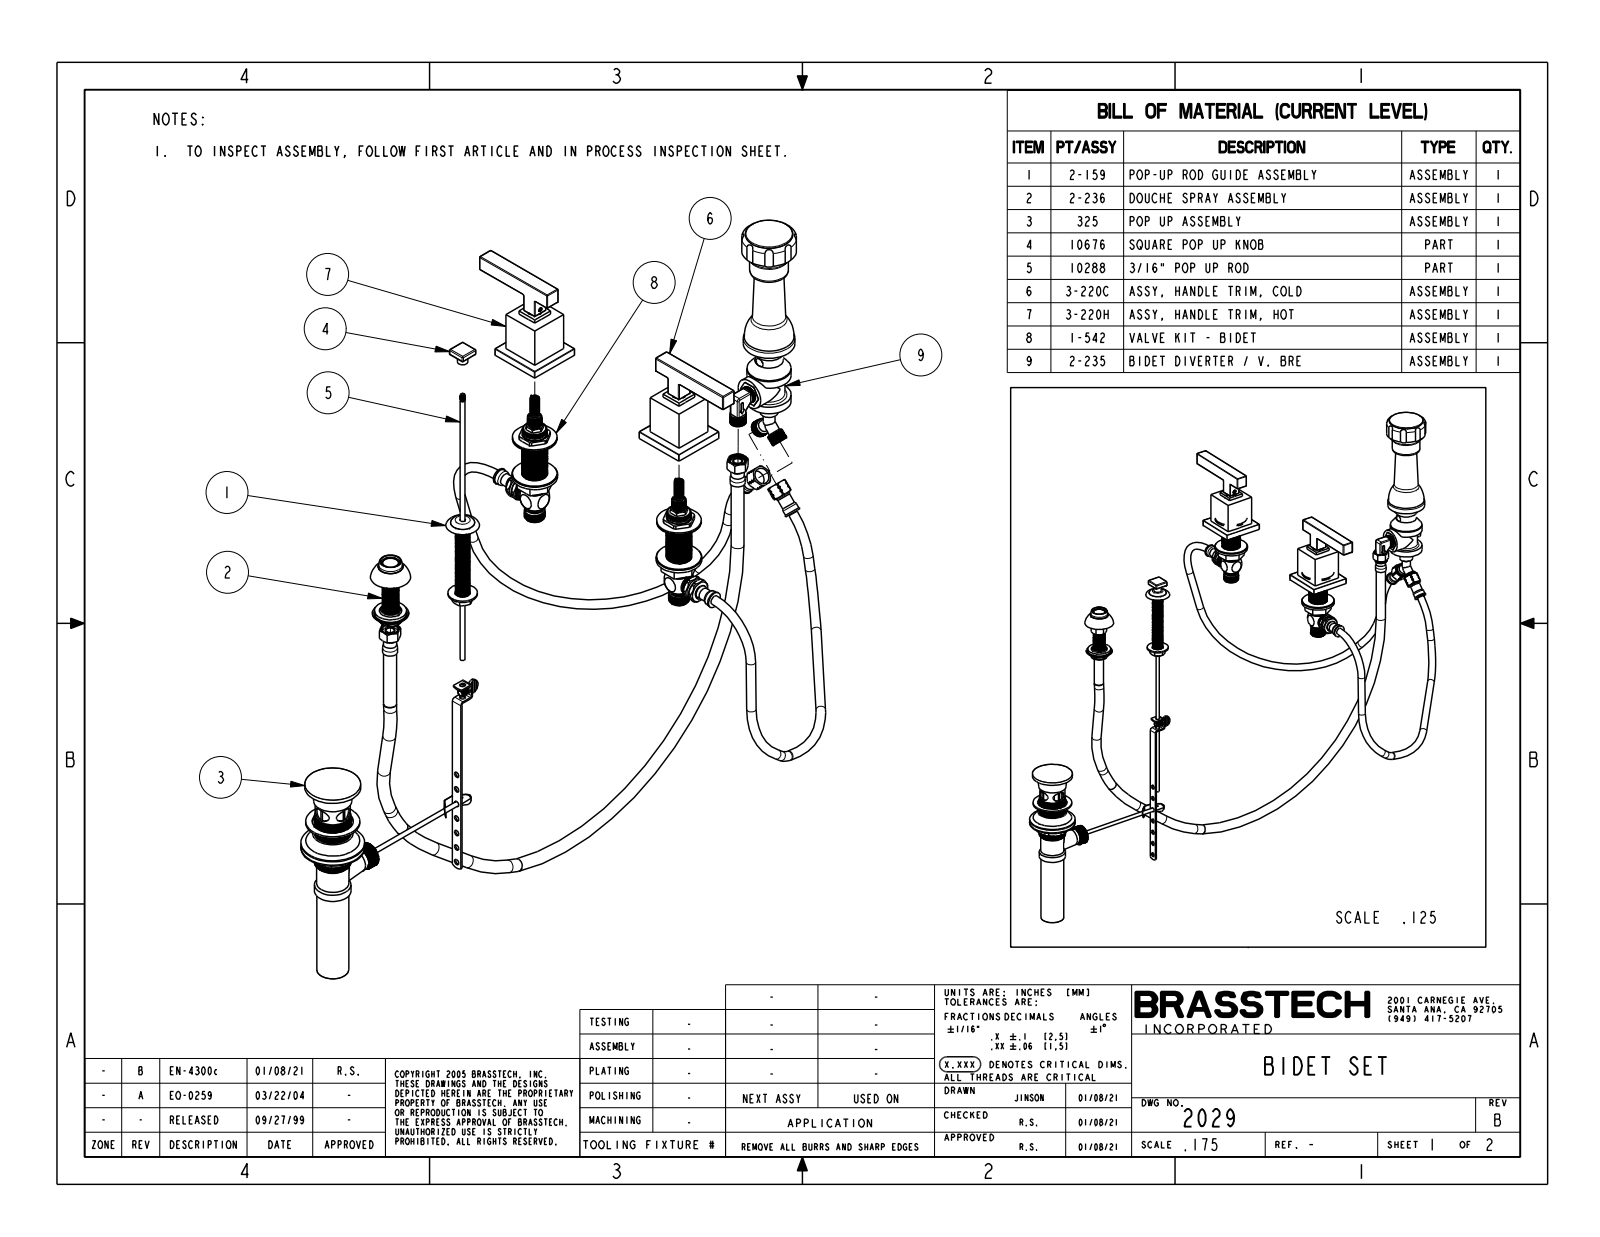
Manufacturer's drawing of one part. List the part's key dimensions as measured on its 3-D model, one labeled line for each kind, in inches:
Part name (STEP PRODUCT): 2029
STEP written by: CREO PARAMETRIC BY PTC INC, 2018400 (CONFIG_CONTROL_DESIGN)
Units: inches
Bodies: 5 solids, 315 faces (97 planar, 124 cylindrical, 94 other)
Overall size (bounding box): 22.855 × 13.52 × 5.353
Volume: 27.39 in³ · Surface area: 120.4 in²
Round holes (diameter × count): ⌀0.625 ×1, ⌀0.792 ×1, ⌀0.94 ×1
Round bosses / shafts (diameter × count): ⌀0.4 ×3, ⌀0.673 ×2, ⌀2.025 ×1, ⌀1.52 ×1, ⌀0.925 ×1, ⌀0.775 ×1
Partial cylindrical surfaces — rounded edges, fillets, slot ends (radius × count): R0.03 ×38, R0.02 ×14, R0.04 ×12, R0.21 ×8, R0.357 ×1, R1.077 ×1
Main face-to-face distances: 0.487, 1.113, 1.6, 0.31, 8, 0.625, 1.91, 1.95, 1.64, 3.515
